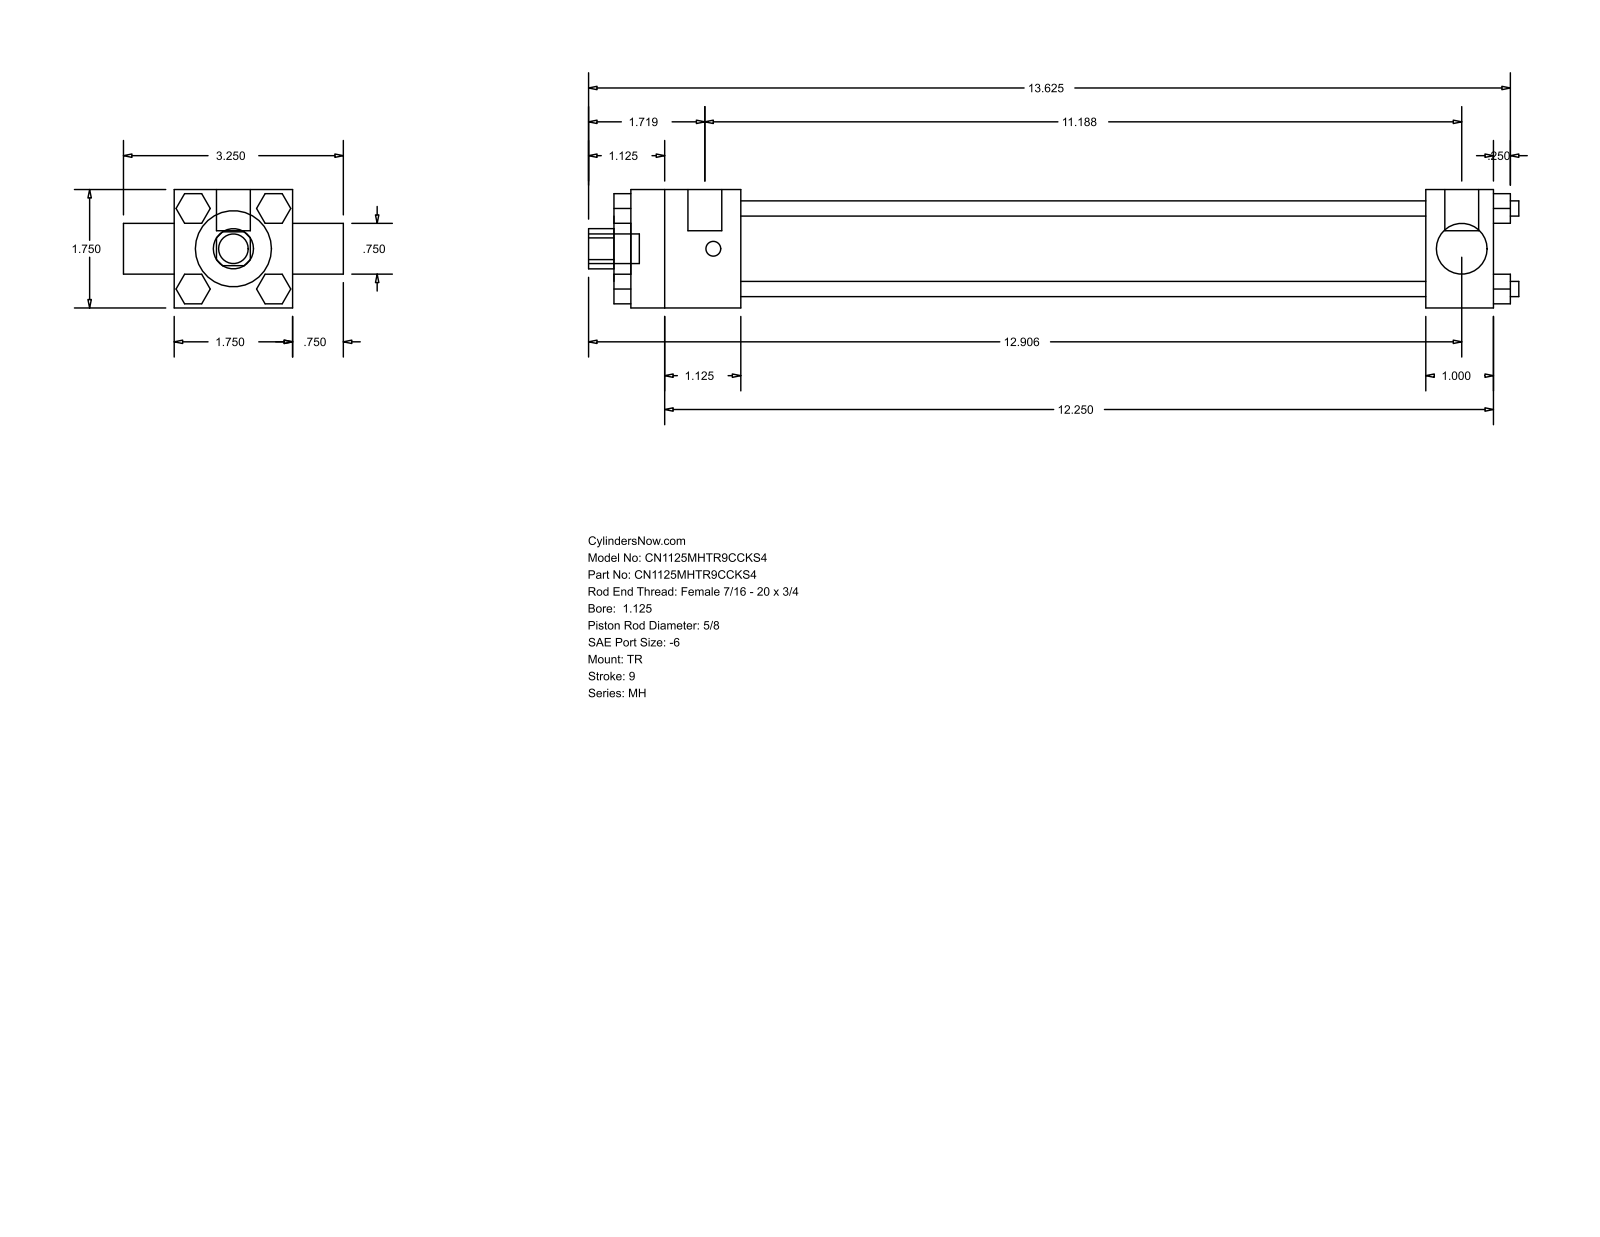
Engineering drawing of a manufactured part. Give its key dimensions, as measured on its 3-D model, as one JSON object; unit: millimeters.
{"part_name": "MH_TR__0112_0.625", "step_written_by": "GSSL Pune (CONFIG_CONTROL_DESIGN)", "units": "millimeters", "bodies": {"solids": 0, "faces": 120, "planar": 92, "cylindrical": 28, "other": 0}, "overall_size": [349.25, 82.55, 44.45], "round_holes": [[15.88, 1], [19.05, 1], [28.57, 1], [34.92, 1]], "round_bosses_or_shafts": [[5.71, 4], [5.56, 3], [12.7, 2], [11.11, 1]], "partial_cylinders_radius": [[7.54, 1]], "face_to_face_distances": [44.46, 11.11, 257.17, 282.58, 25.41, 41.27, 298.44, 323.85, 47.62, 330.2]}
